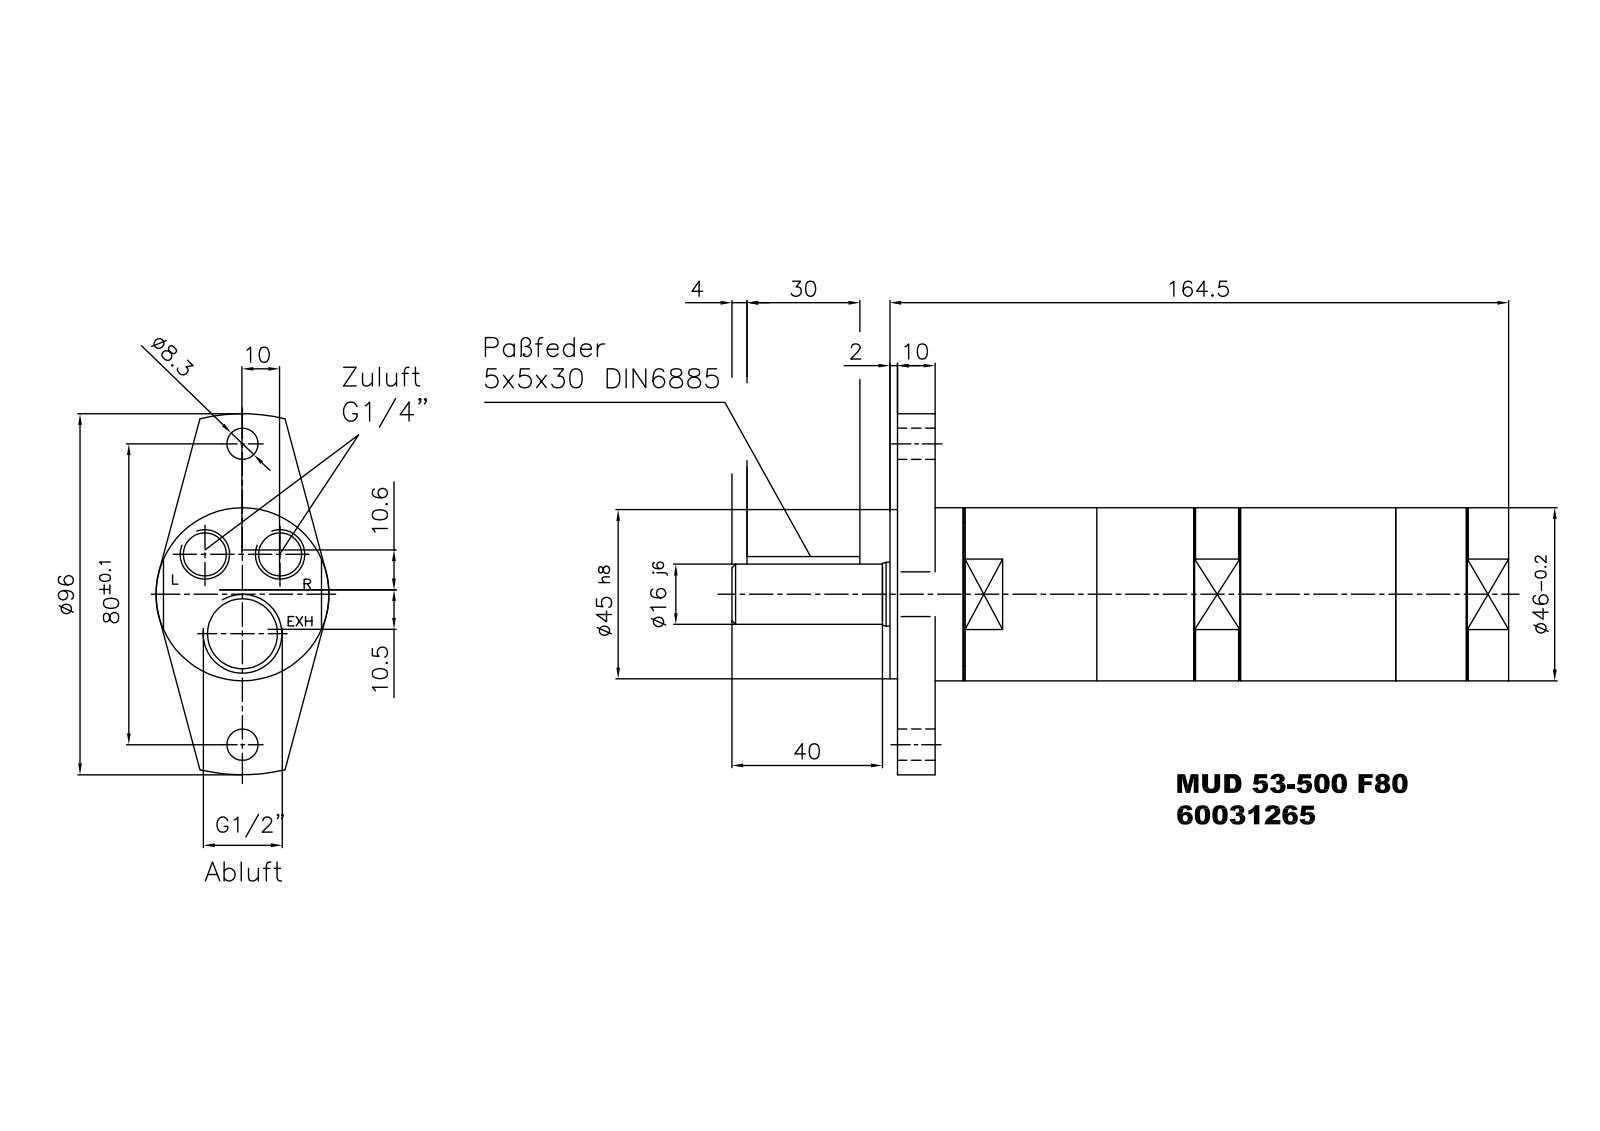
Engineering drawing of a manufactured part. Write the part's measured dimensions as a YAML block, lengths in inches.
part_name: "MUD 53-500 390 220 F80 206,5mm"
step_written_by: "Autodesk Inventor 2013 (AUTOMOTIVE_DESIGN)"
units: inches
bodies: {solids: 1, faces: 185, planar: 119, cylindrical: 24, other: 42}
overall_size: [8.13, 3.78, 1.811]
volume: 17.64
surface_area: 58.37
round_holes:
  - {diameter: 0.327, count: 2}
  - {diameter: 0.451, count: 2}
  - {diameter: 0.063, count: 1}
  - {diameter: 0.689, count: 1}
  - {diameter: 0.733, count: 1}
round_bosses_or_shafts:
  - {diameter: 1.811, count: 1}
  - {diameter: 1.772, count: 1}
  - {diameter: 1.575, count: 1}
  - {diameter: 0.667, count: 1}
  - {diameter: 0.63, count: 1}
partial_cylinders:
  - {radius: 0.098, count: 2}
  - {radius: 1.89, count: 1}
face_to_face_distances: [0.394, 0.472, 0.079, 6.004, 6.476, 6.398, 5.217, 1.181, 5.295, 0.689]
hole_center_spacings: [0.574, 0.919, 1.222, 1.575, 2.031, 0.413, 0.787, 1.161]
